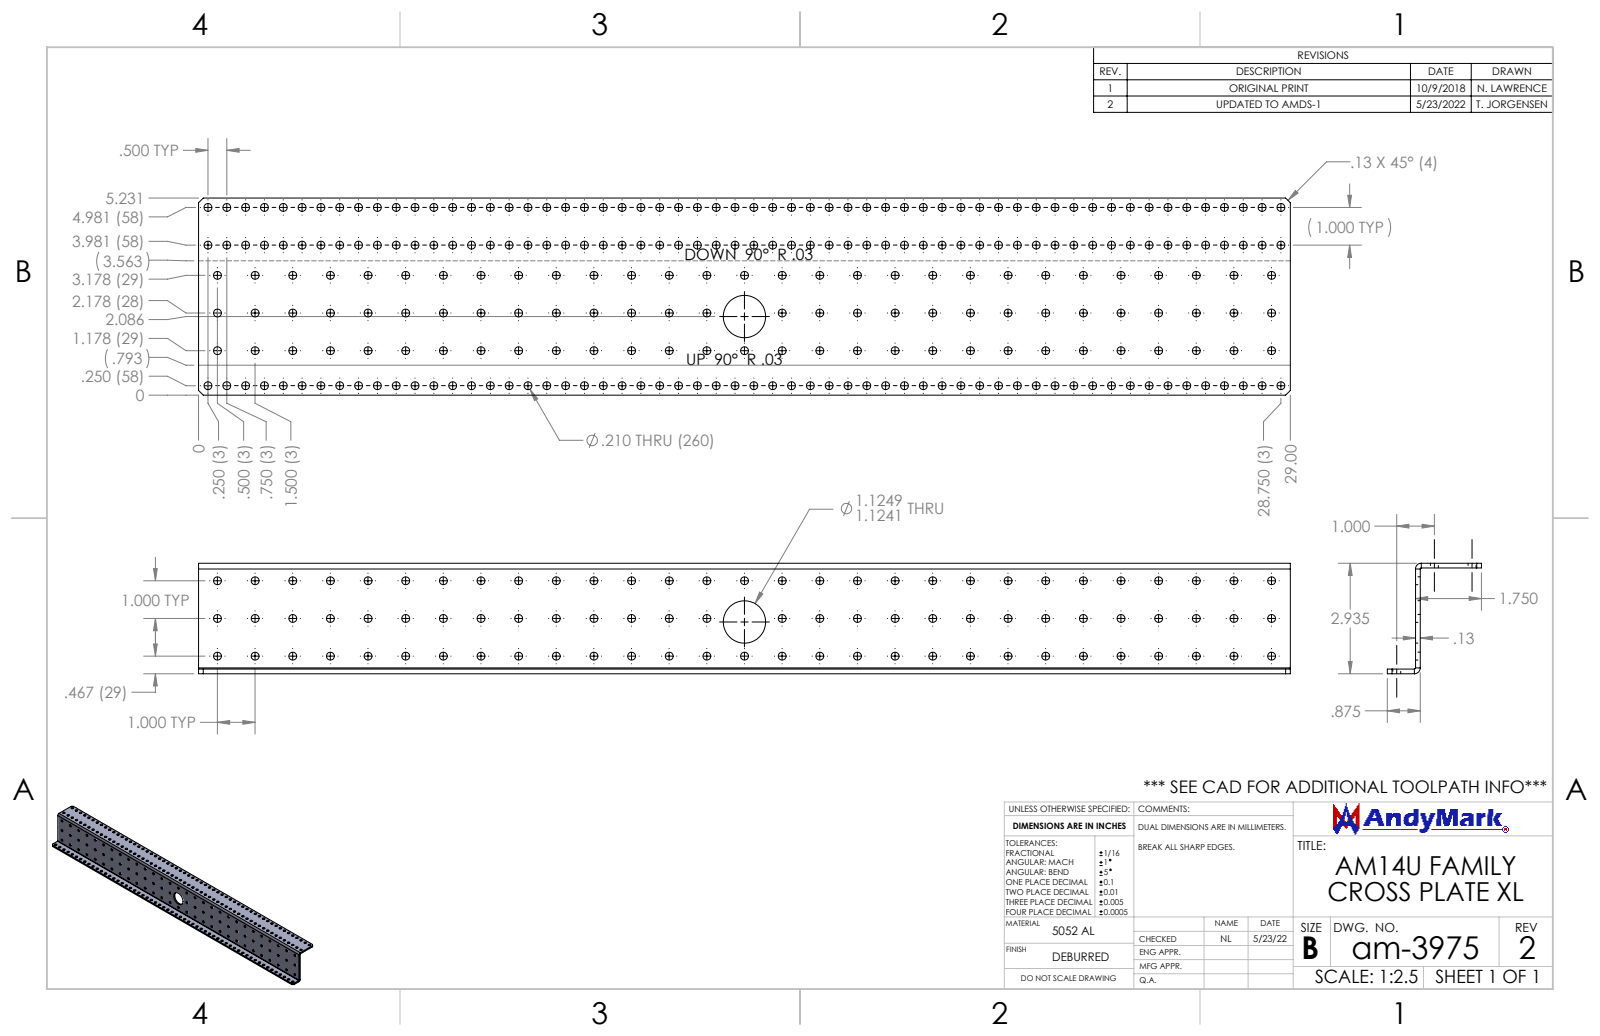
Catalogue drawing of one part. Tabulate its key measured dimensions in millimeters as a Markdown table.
| quantity | value |
| --- | --- |
| part name | am-3975 AM14U Family Cross Plate XL |
| STEP written by | SolidWorks 2021 (CONFIG_CONTROL_DESIGN) |
| units | millimeters |
| bodies | 1 solid, 548 faces (22 planar, 526 cylindrical, 0 other) |
| overall size | 736.6 × 74.5 × 63.5 |
| volume | 290 200 mm³ |
| surface area | 202 400 mm² |
| round holes (diameter × count) | 5.3 × 260, 28.6 × 1 |
| partial cylindrical surfaces (radius × count) | 0.7 × 2, 3.9 × 2 |
| main face-to-face distances | 3.2, 3.2, 71.3, 74.5, 68.2, 71.4, 22.2, 19.1, 41.3, 44.5 |
| hole center spacings | 25.4, 56.8, 35.9, 50.8, 80.3, 76.2, 104.7, 101.6 |
